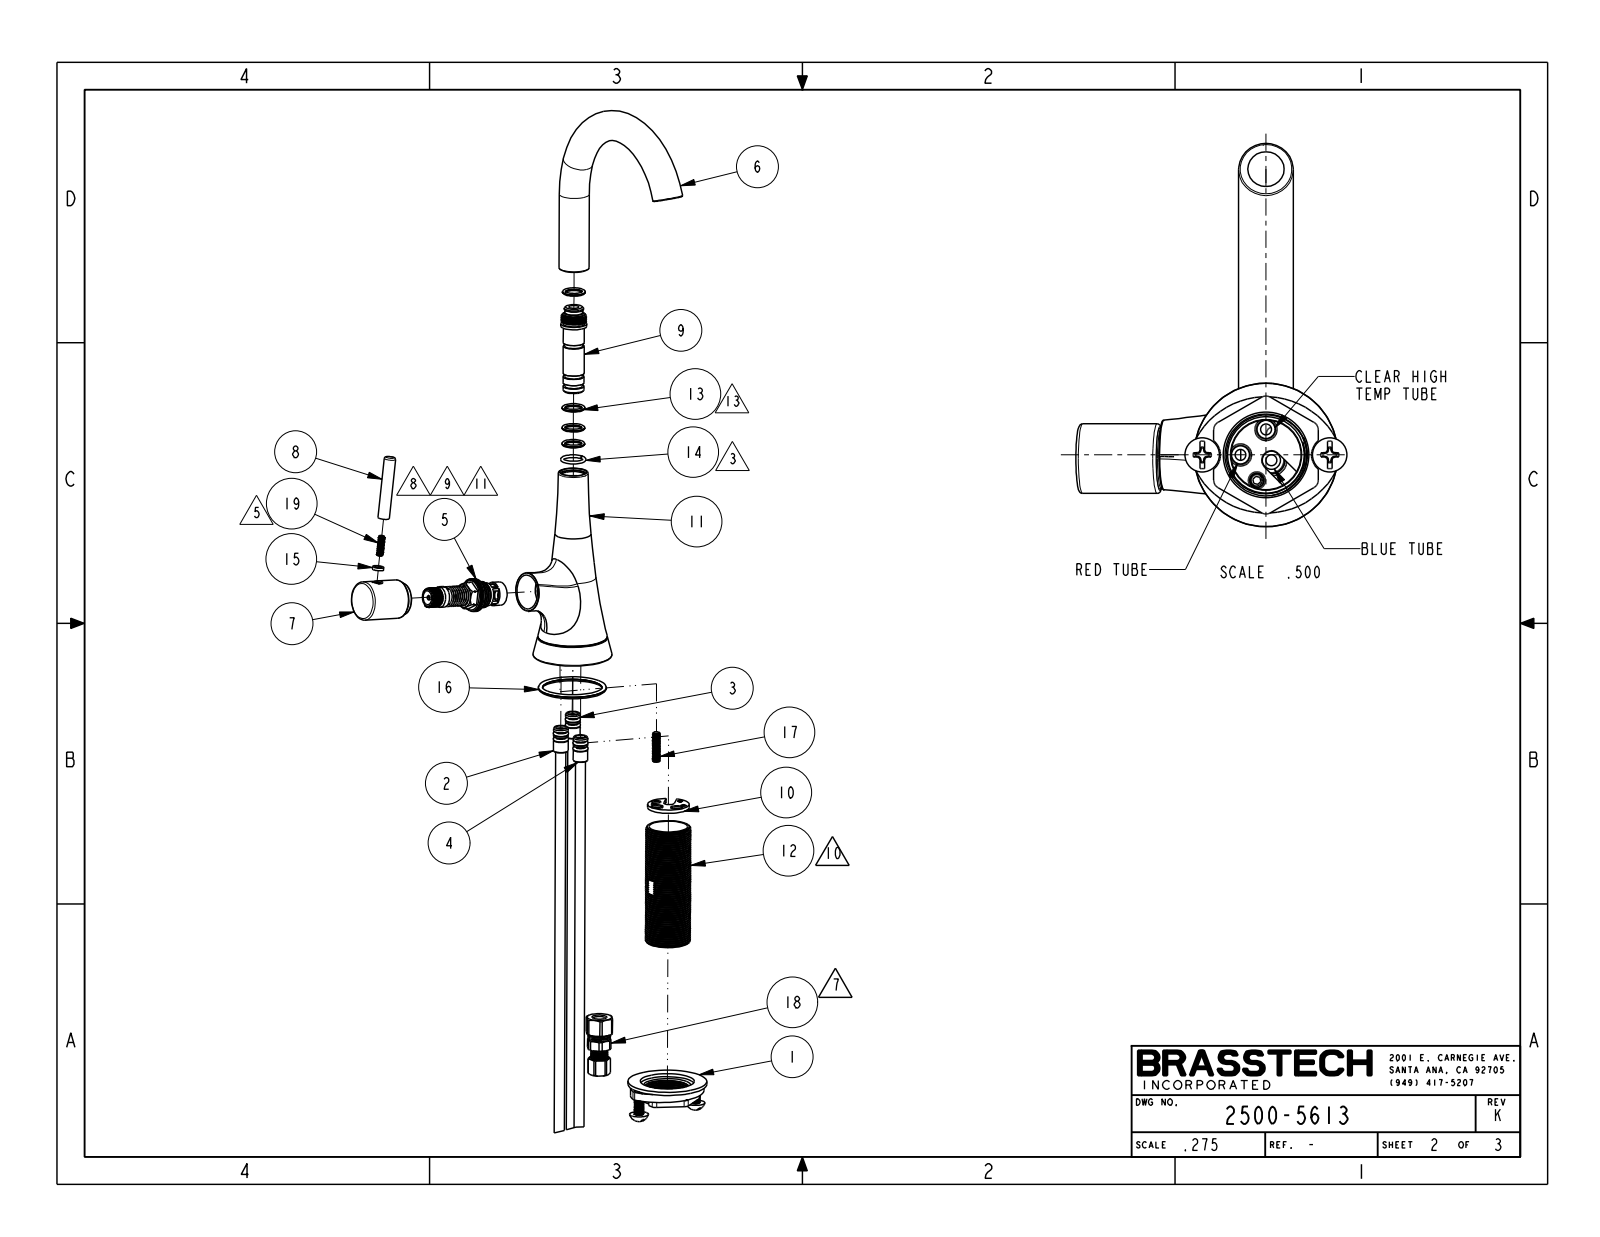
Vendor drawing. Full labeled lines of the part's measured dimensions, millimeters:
Part name (STEP PRODUCT): 2500-5613
STEP written by: CREO PARAMETRIC BY PTC INC, 2018400 (CONFIG_CONTROL_DESIGN)
Units: millimetres
Bodies: 1 solid, 70 faces (10 planar, 18 cylindrical, 42 other)
Overall size (bounding box): 236.5 × 133.9 × 91.4
Volume: 176 200 mm³ · Surface area: 30 680 mm²
Round holes (diameter × count): ⌀7.4 ×1
Round bosses / shafts (diameter × count): ⌀24.4 ×2, ⌀43.7 ×1, ⌀20.7 ×1, ⌀19.1 ×1, ⌀15.9 ×1, ⌀7.2 ×1, ⌀7.1 ×1
Main face-to-face distances: 29.3, 121.5, 121.2, 0.4, 28.2, 1.1, 41.3, 1.7, 39.6
